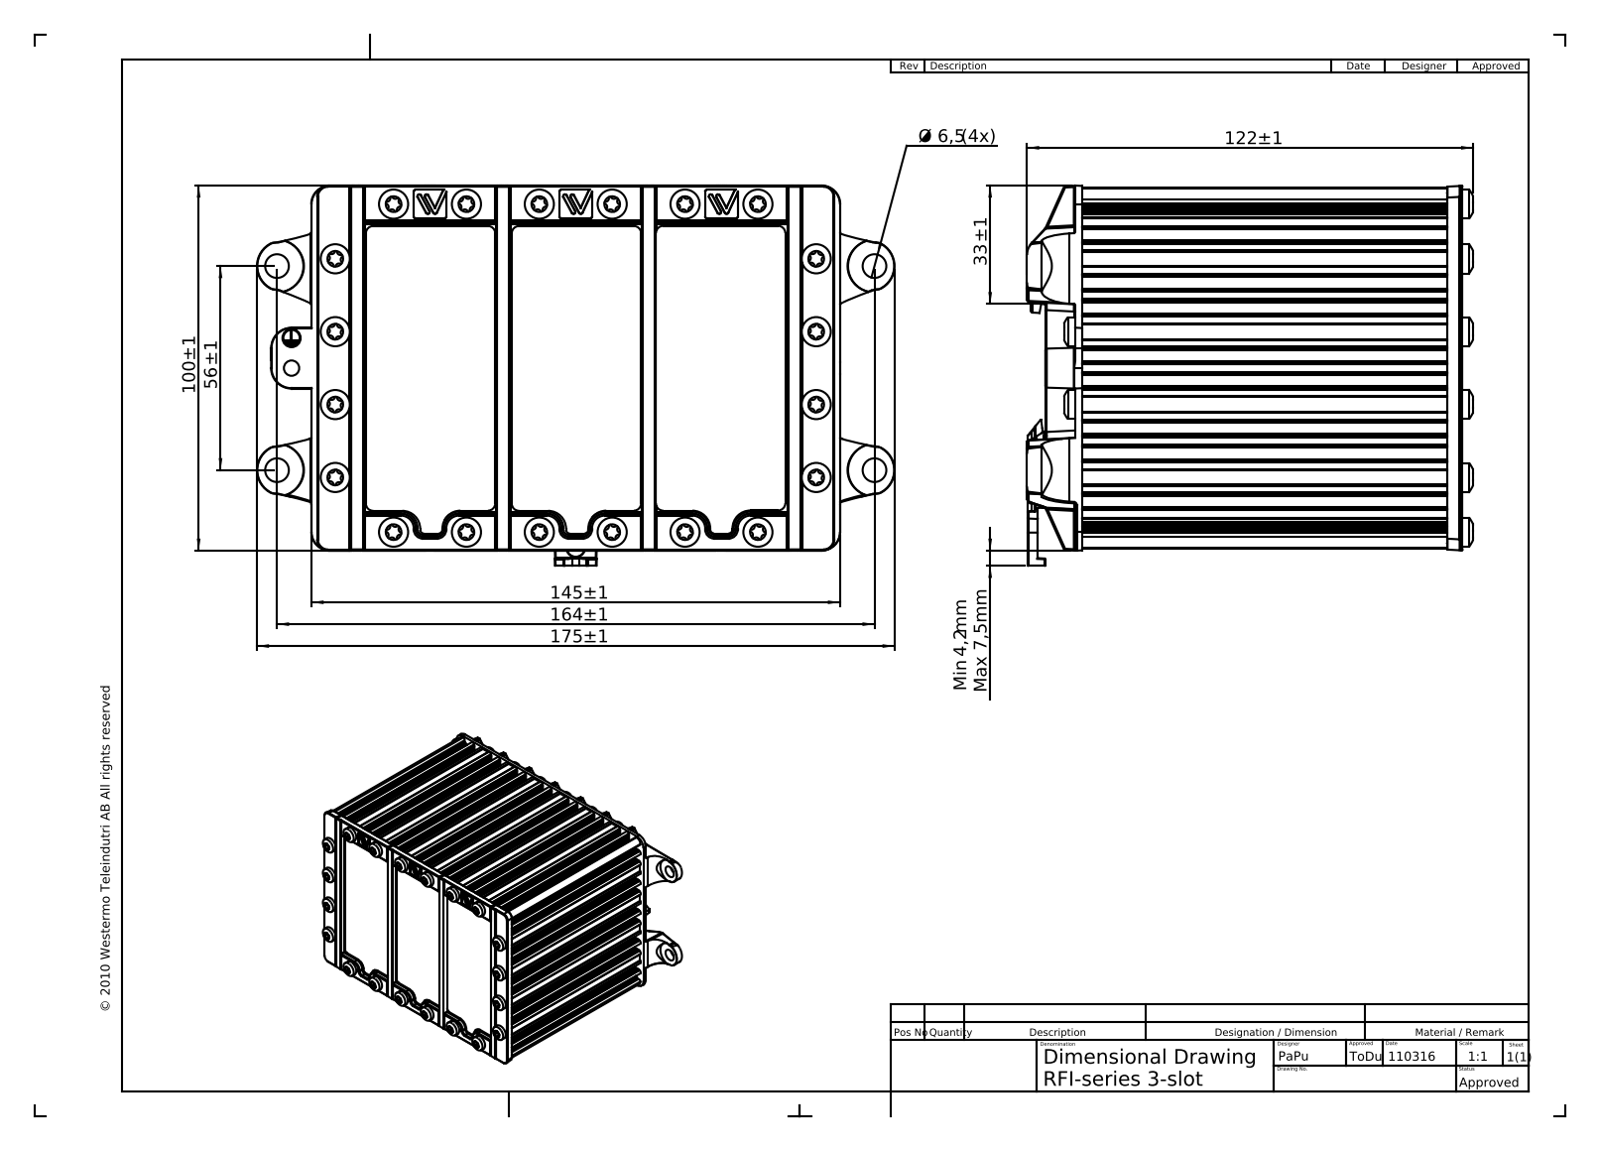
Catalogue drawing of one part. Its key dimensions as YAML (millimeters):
part_name: "Redfox_Industrial_RFI-18-F4G; 2010-4221_4tx_gigab; RJ45 1X4 gigabit MagJack; 1X4 gigabit MagJack (+8 more)"
step_written_by: "SolidWorks 2011 (CONFIG_CONTROL_DESIGN)"
units: millimeters
bodies: {solids: 82, faces: 21628, planar: 6394, cylindrical: 6102, other: 9132}
overall_size: [174.99, 122.4, 104.36]
volume: 619152
surface_area: 462636
round_holes:
  - {diameter: 2, count: 79}
  - {diameter: 0.97, count: 60}
  - {diameter: 2.5, count: 26}
  - {diameter: 3.3, count: 20}
  - {diameter: 0.27, count: 8}
  - {diameter: 0.92, count: 6}
  - {diameter: 0.97, count: 4}
  - {diameter: 1.25, count: 4}
  - {diameter: 1.3, count: 4}
  - {diameter: 1.52, count: 4}
  - {diameter: 6.5, count: 4}
  - {diameter: 1.73, count: 3}
round_bosses_or_shafts:
  - {diameter: 4, count: 23}
  - {diameter: 8, count: 20}
  - {diameter: 1.27, count: 20}
  - {diameter: 1, count: 10}
  - {diameter: 1.27, count: 7}
  - {diameter: 1.6, count: 5}
  - {diameter: 1.2, count: 4}
  - {diameter: 3.5, count: 2}
partial_cylinders:
  - {radius: 0.4, count: 904}
  - {radius: 0.5, count: 430}
  - {radius: 0.2, count: 299}
  - {radius: 0.29, count: 240}
  - {radius: 0.99, count: 240}
  - {radius: 1, count: 127}
  - {radius: 0.3, count: 116}
  - {radius: 0.25, count: 104}
face_to_face_distances: [40, 1.6, 80, 32.29, 30.69, 5.31, 36, 3.71, 4, 11.56]
hole_center_spacings: [3.99, 7.98, 11.97, 15.96, 19.95, 23.94, 27.93, 31.92]
